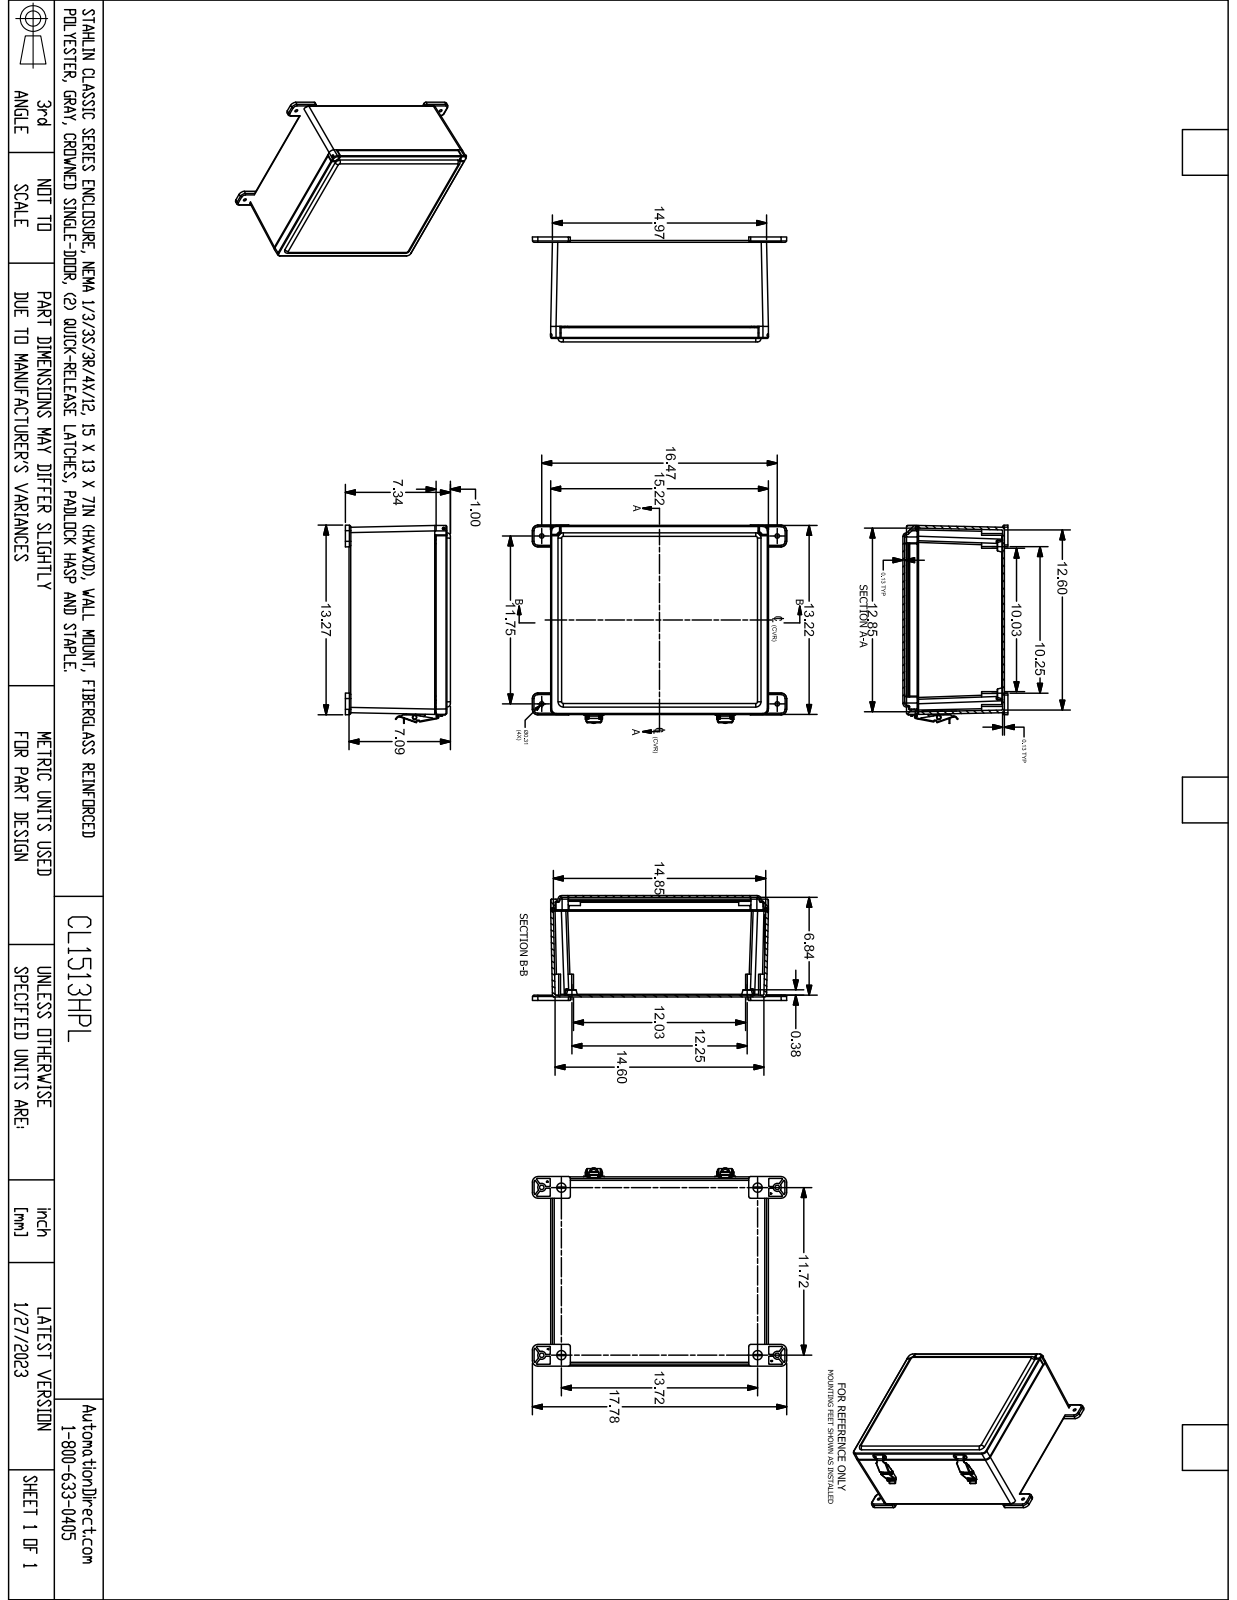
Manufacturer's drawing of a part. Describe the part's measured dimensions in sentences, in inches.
The part is named "CE1513HPL". Its 3-D file was written by "SolidWorks 2018 (AUTOMOTIVE_DESIGN)". It is 47 solids with 1796 faces: 795 planar, 592 cylindrical and 409 other. Overall it measures 17.782 by 13.873 by 7.344 inches. Its volume is 144.1 cubic inches and its surface area 1 762 square inches. Round holes: 8 of diameter 0.104, 8 of diameter 0.14, 6 of diameter 0.159, 6 of diameter 0.281, 4 of diameter 0.13, 4 of diameter 0.13, 4 of diameter 0.313, 4 of diameter 0.313, 4 of diameter 0.344, 4 of diameter 0.531, 2 of diameter 0.096, 2 of diameter 0.114. Round bosses or shafts: 6 of diameter 0.27, 6 of diameter 0.125, 4 of diameter 0.229, 4 of diameter 0.125, 2 of diameter 0.375, 2 of diameter 0.325, 2 of diameter 0.182, 2 of diameter 0.127. Partial cylindrical surfaces (rounded edges, fillets, slot ends): 60 of radius 0.031, 56 of radius 0.031, 44 of radius 0.125, 23 of radius 0.062, 16 of radius 0.045, 16 of radius 0.25, 12 of radius 0.03, 12 of radius 0.1. The main face-to-face distances are 0.125, 6.969, 0.186, 7.094, 6.844, 0.125, 0.25, 6.844, 6.719, 0.75. The hole center spacings are 9.188, 0.75, 9.219, 1.039, 1.046, 1.375, 2.238, 11.01.
